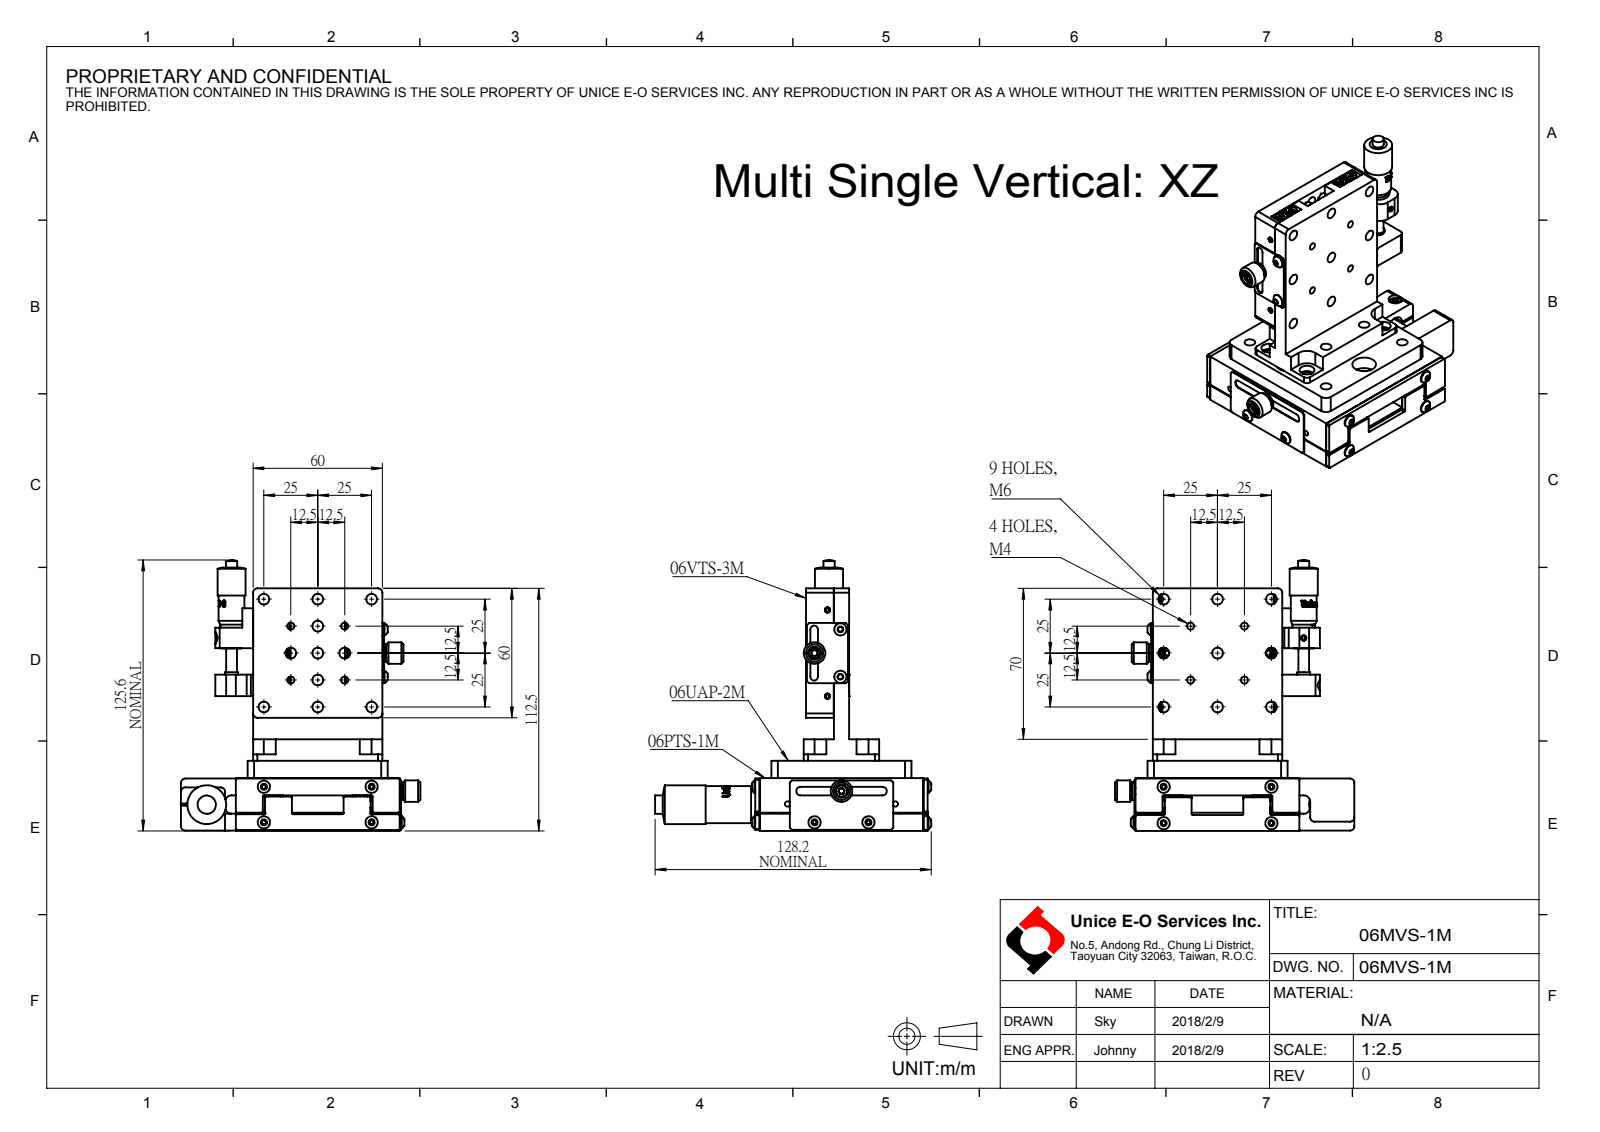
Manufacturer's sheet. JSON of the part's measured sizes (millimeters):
{"part_name": "06MVS-1M", "step_written_by": "SolidWorks 2016 (AUTOMOTIVE_DESIGN)", "units": "millimeters", "bodies": {"solids": 0, "faces": 1005, "planar": 477, "cylindrical": 390, "other": 138}, "overall_size": [128.15, 125.65, 111.1], "round_holes": [[2.5, 27], [5, 27], [3.3, 8], [6.5, 7], [7, 4], [11, 4], [6.7, 3], [6, 2], [9.5, 1], [10, 1]], "round_bosses_or_shafts": [[5.7, 10], [5, 5], [6, 3], [10, 2], [8, 2], [5.5, 2], [4.5, 2], [2.5, 2]], "partial_cylinders_radius": [[0.5, 32], [2, 20], [3, 6], [5, 4], [5.5, 4], [1.75, 2], [2.5, 1], [5.98, 1]], "face_to_face_distances": [8, 16, 41.5, 34.5, 20, 24.5, 16.5, 7, 76, 13], "hole_center_spacings": [17.68, 25, 27.95, 39.53, 12.5, 50, 10, 35.36]}
